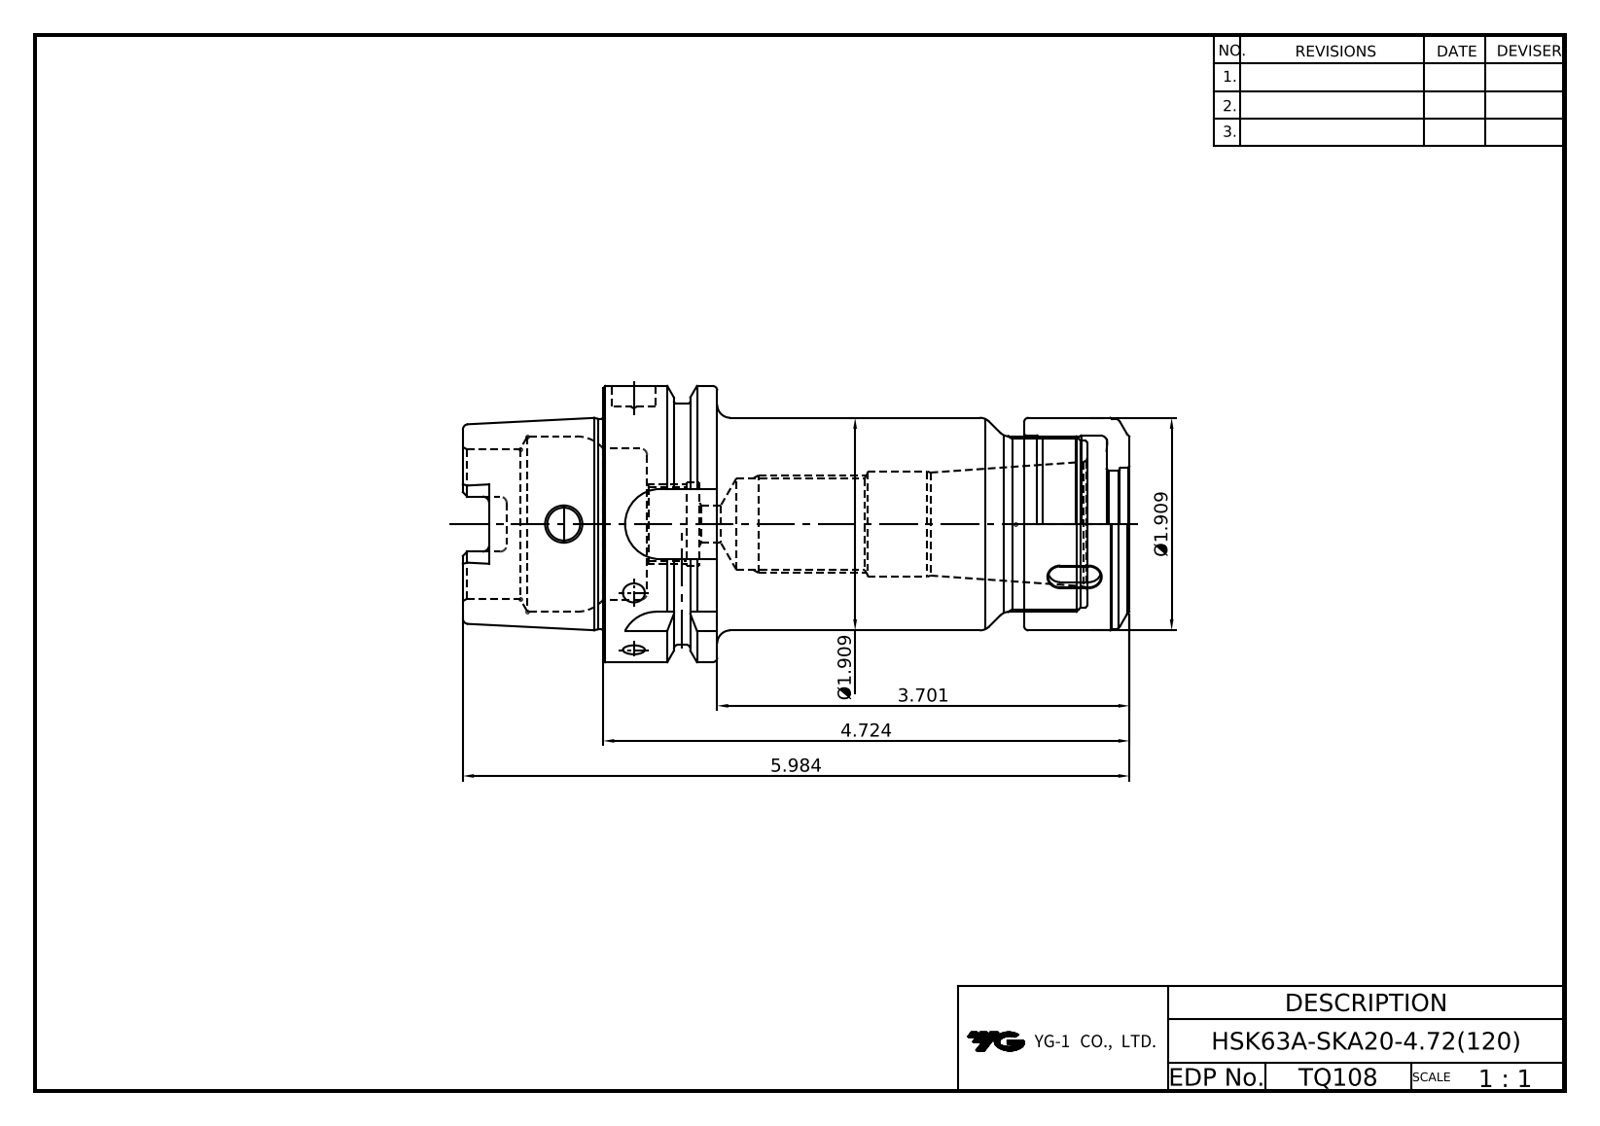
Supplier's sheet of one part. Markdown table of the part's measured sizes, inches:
| quantity | value |
| --- | --- |
| part name | LO-HSK63A-SKA20-120; SKN20-NUT |
| STEP written by | Autodesk Inventor 2024 (AUTOMOTIVE_DESIGN) |
| units | inches |
| bodies | 2 solids, 202 faces (67 planar, 54 cylindrical, 81 other) |
| overall size | 5.984 × 2.48 × 2.48 |
| volume | 12.51 in³ |
| surface area | 74.94 in² |
| round holes (diameter × count) | 0.295 × 1, 0.315 × 1, 0.394 × 1, 0.666 × 1, 0.748 × 1, 0.807 × 1, 0.945 × 1, 1.15 × 1, 1.22 × 1, 1.339 × 1, 1.532 × 1, 1.575 × 1 |
| round bosses / shafts (diameter × count) | 2.48 × 1, 2.165 × 1, 1.909 × 1, 1.894 × 1, 1.891 × 1, 1.496 × 1 |
| partial cylindrical surfaces (radius × count) | 0.059 × 6, 0.113 × 4, 0.315 × 4 |
| main face-to-face distances | 0.63, 3.386, 0.394, 1.024, 3.701, 4.724, 4.331, 0.472, 1.26, 0.157 |
